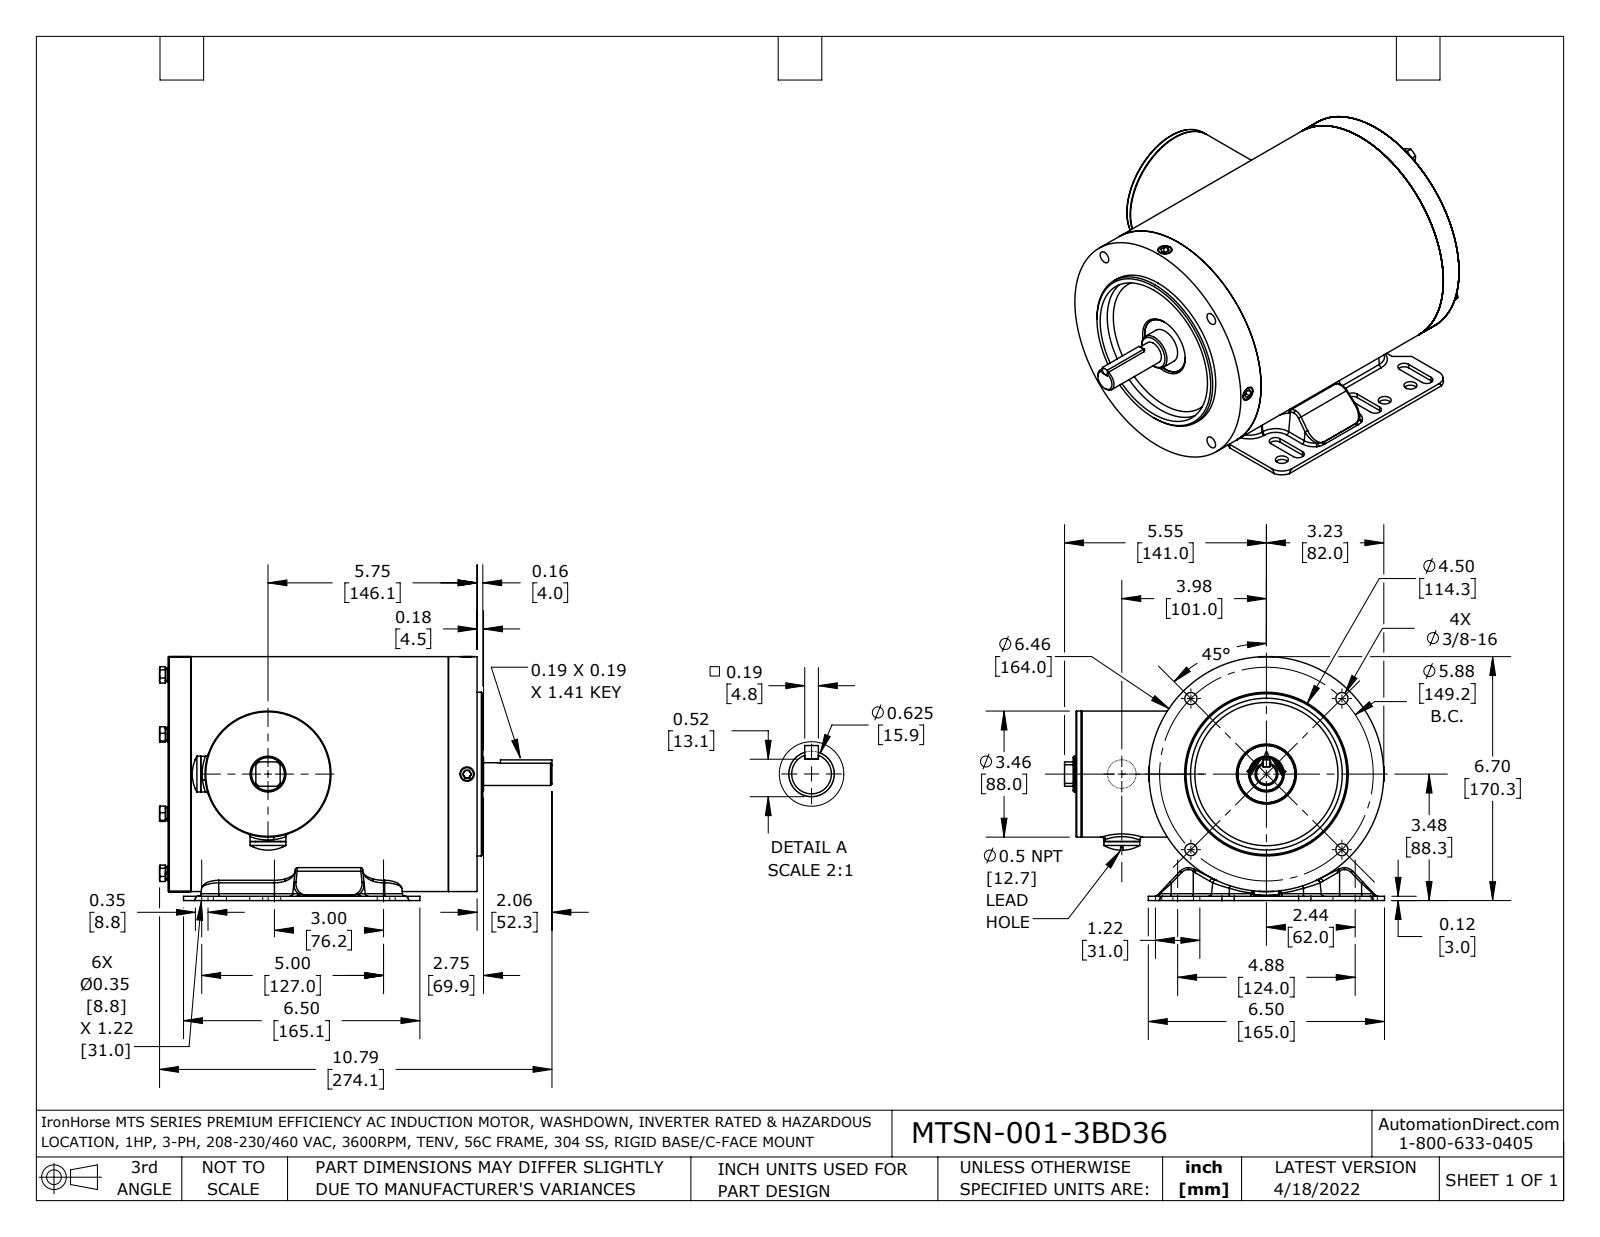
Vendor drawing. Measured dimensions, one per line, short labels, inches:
name: A(MTSN-001-3BD18) nc WITH - bolts redcmb1 coord fxt
written by: SolidWorks 2021 (AUTOMOTIVE_DESIGN)
unit: in
bodies: 8 solids, 925 faces (286 planar, 323 cylindrical, 316 other)
size: 10.791 × 8.799 × 6.705
volume: 50.18 in³; area: 738 in²
holes: 6× ⌀0.165, 6× ⌀0.358, 4× ⌀0.256, 4× ⌀0.335, 2× ⌀0.118, 2× ⌀0.656, 2× ⌀1.378, 1× ⌀0.209, 1× ⌀1.024, 1× ⌀1.654, 1× ⌀2.047, 1× ⌀2.598
bosses: 6× ⌀0.394, 4× ⌀0.984, 4× ⌀0.315, 4× ⌀0.236, 2× ⌀0.787, 2× ⌀0.692, 1× ⌀6.457, 1× ⌀6.319
rounds: 40× R0.079, 12× R0.173, 6× R0.059, 6× R0.315, 5× R0.118, 4× R0.039, 4× R0.108, 4× R0.197
face distances: 0.118, 8.366, 0.236, 8.248, 8.13, 8.484, 0.354, 8.012, 0.157, 0.433
hole spacings: 2.937, 4.154, 1.181, 2.231, 2.498, 3.234, 3.459, 3.93
